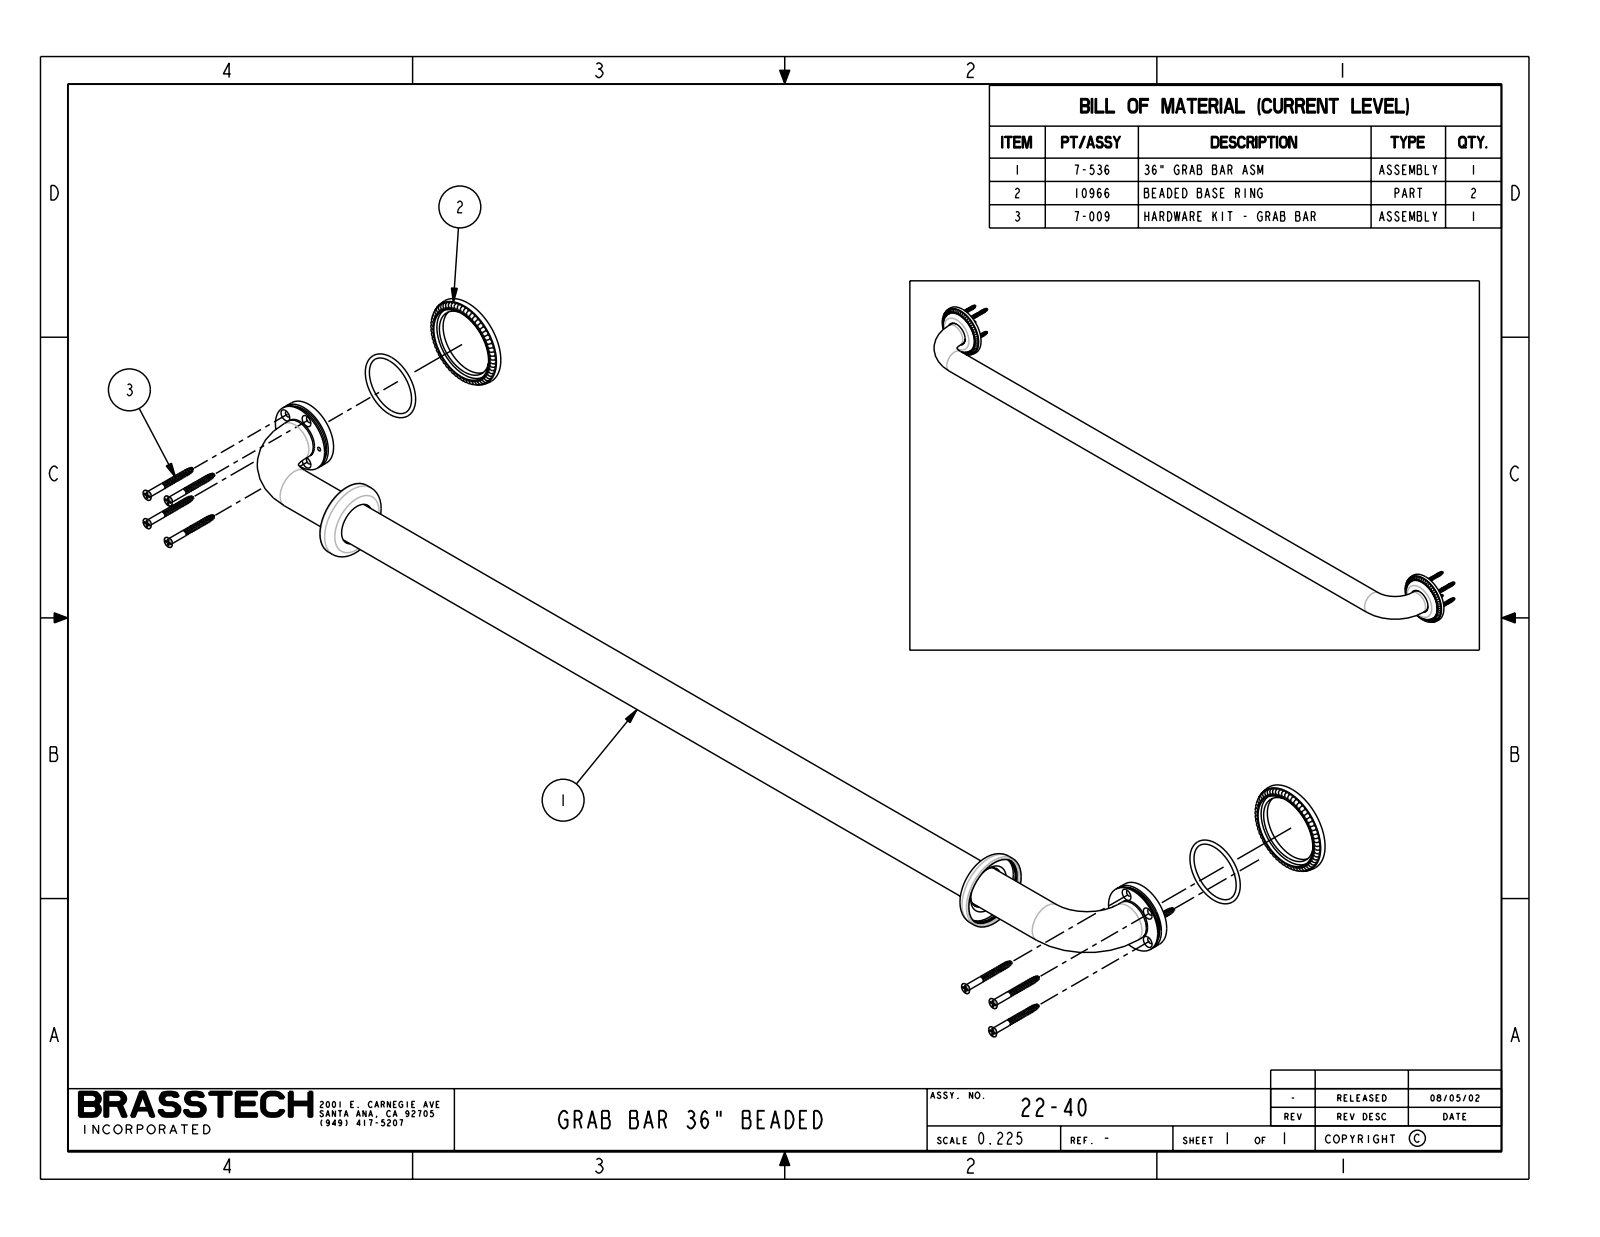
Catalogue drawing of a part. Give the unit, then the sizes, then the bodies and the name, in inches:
Units: inches
Overall size (bounding box): 38.845 × 3.022 × 2.845
Round bosses / shafts (diameter × count): ⌀1.25 ×3
Main face-to-face distances: 0.165, 0.29, 0.125, 0.479, 0.314, 0.189
Bodies: 0 solids, 396 faces (8 planar, 6 cylindrical, 382 other)
Part name (STEP PRODUCT): 22-40_WEB
STEP written by: PRO/ENGINEER BY PARAMETRIC TECHNOLOGY CORPORATION, 2009300 (CONFIG_CONTROL_DESIGN)
